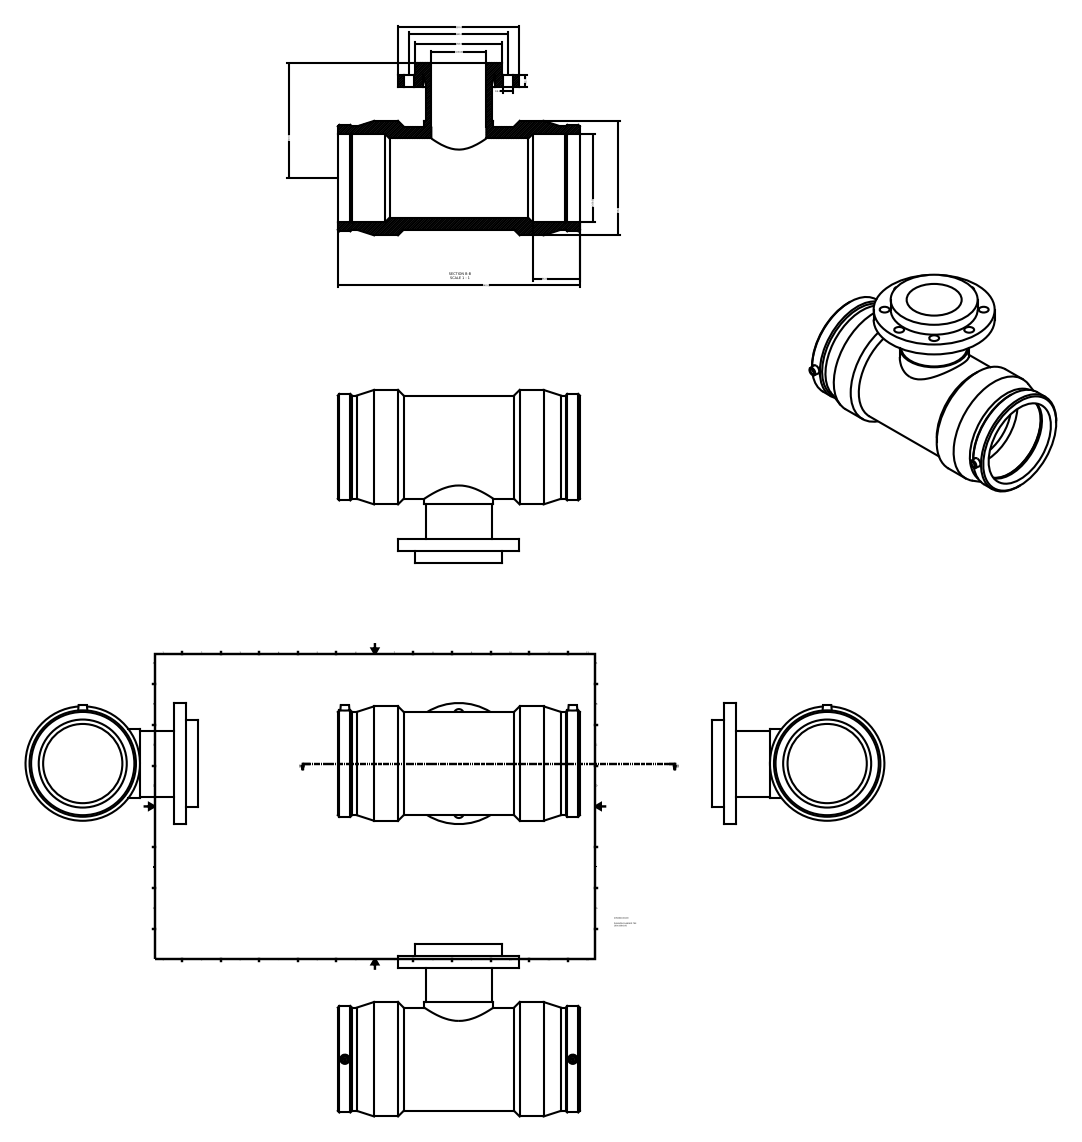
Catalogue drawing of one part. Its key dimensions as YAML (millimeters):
part_name: "499404160100"
step_written_by: "Autodesk Inventor 2015 (AUTOMOTIVE_DESIGN)"
units: millimeters
bodies: {solids: 1, faces: 60, planar: 14, cylindrical: 30, other: 16}
overall_size: [440, 314, 220]
volume: 6153000
surface_area: 670140
round_holes:
  - {diameter: 18, count: 8}
  - {diameter: 10, count: 2}
  - {diameter: 100, count: 1}
  - {diameter: 130, count: 1}
  - {diameter: 144, count: 1}
  - {diameter: 160, count: 1}
round_bosses_or_shafts:
  - {diameter: 4, count: 2}
  - {diameter: 220, count: 1}
  - {diameter: 208, count: 1}
  - {diameter: 193.44, count: 1}
  - {diameter: 187.64, count: 1}
  - {diameter: 187.2, count: 1}
  - {diameter: 158, count: 1}
  - {diameter: 125, count: 1}
face_to_face_distances: [22, 44, 440, 106, 84, 62, 26.42, 413.58, 387.16, 14]
hole_center_spacings: [68.88, 90, 127.28, 166.3, 180, 414.2]
